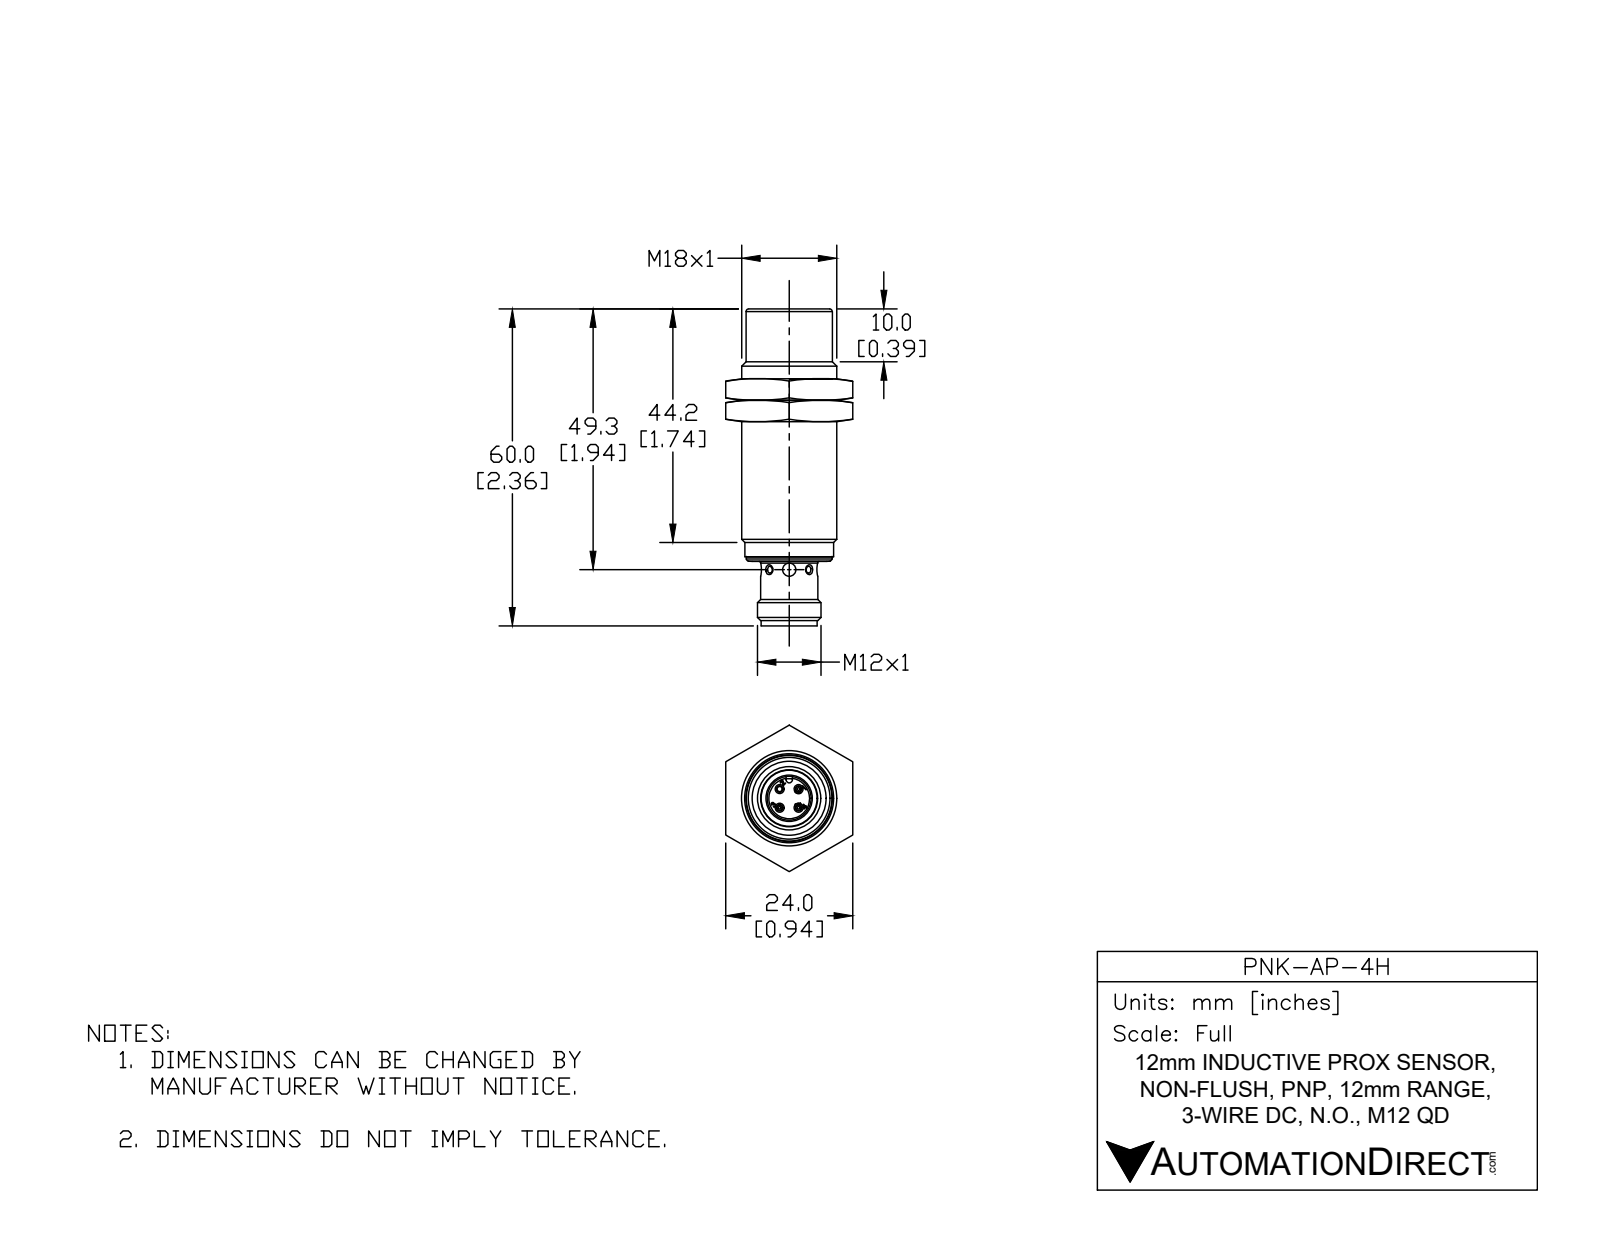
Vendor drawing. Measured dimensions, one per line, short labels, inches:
name: PNK-AP-4H
written by: SolidWorks 2017 (AUTOMOTIVE_DESIGN)
unit: in
bodies: 1 solid, 1142 faces (751 planar, 150 cylindrical, 241 other)
size: 2.362 × 0.709 × 0.709
volume: 0.746 in³; area: 14.66 in²
holes: 3× ⌀0.043, 2× ⌀0.04, 2× ⌀0.098, 1× ⌀0.038, 1× ⌀0.04, 1× ⌀0.327, 1× ⌀0.394, 1× ⌀0.618, 1× ⌀0.634
bosses: 9× ⌀0.039, 1× ⌀0.709, 1× ⌀0.654, 1× ⌀0.638, 1× ⌀0.633, 1× ⌀0.616, 1× ⌀0.608, 1× ⌀0.599
rounds: 38× R0.004, 1× R0.024, 1× R0.031, 1× R0.161
face distances: 0.039, 0.022, 0.018, 1.87, 1.882, 1.86, 1.843, 1.848, 1.831, 2.323
hole spacings: 0.098, 0.139, 0.197
